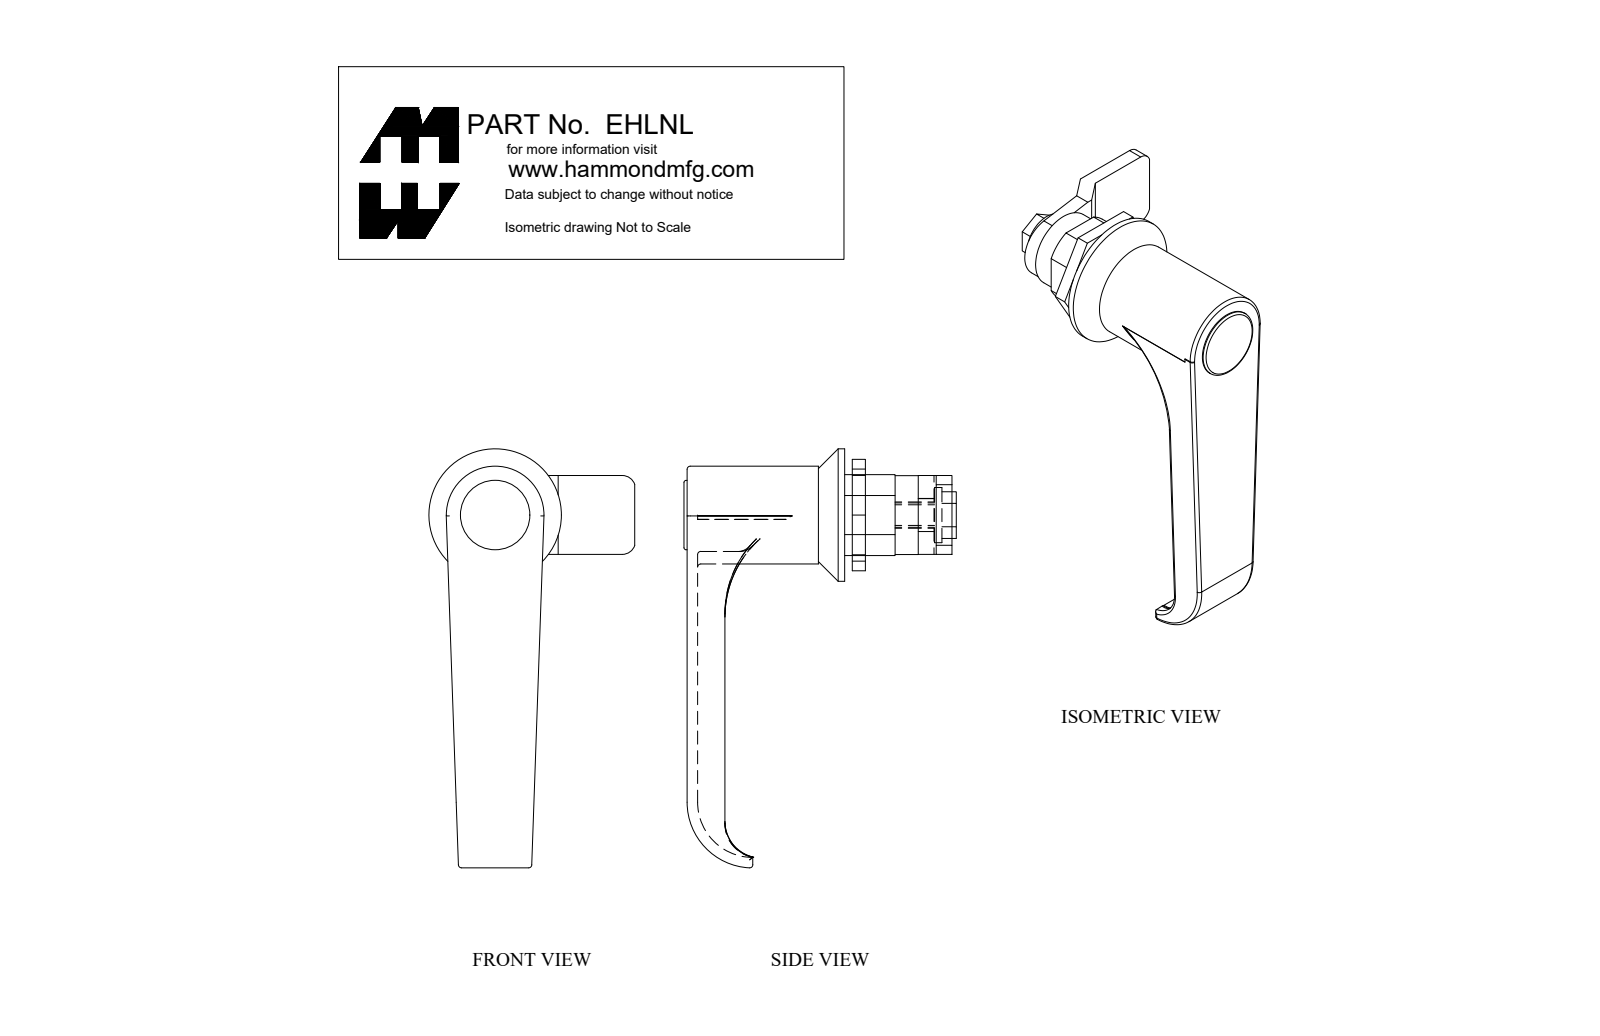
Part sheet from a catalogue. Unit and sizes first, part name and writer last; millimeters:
Units: millimetres
Overall size (bounding box): 101.2 × 65.8 × 49.8
Round holes (diameter × count): ⌀5 ×1, ⌀19.2 ×1
Round bosses / shafts (diameter × count): ⌀32 ×1, ⌀23.6 ×1, ⌀19.1 ×1, ⌀16.8 ×1, ⌀13.3 ×1, ⌀5.9 ×1
Partial cylindrical surfaces — rounded edges, fillets, slot ends (radius × count): R0.8 ×15, R3.2 ×2, R7.8 ×1, R8.3 ×1, R8.9 ×1, R10.8 ×1, R13.3 ×1, R15.9 ×1
Main face-to-face distances: 2.5, 3.8, 4.3, 35.6, 38.1, 17.8, 53.3, 55.9, 8.2, 25.9
Volume: 35 530 mm³ · Surface area: 15 080 mm²
Bodies: 4 solids, 148 faces (64 planar, 48 cylindrical, 36 other)
Part name (STEP PRODUCT): EHLNL_Default
STEP written by: SolidWorks 2018 (CONFIG_CONTROL_DESIGN)
